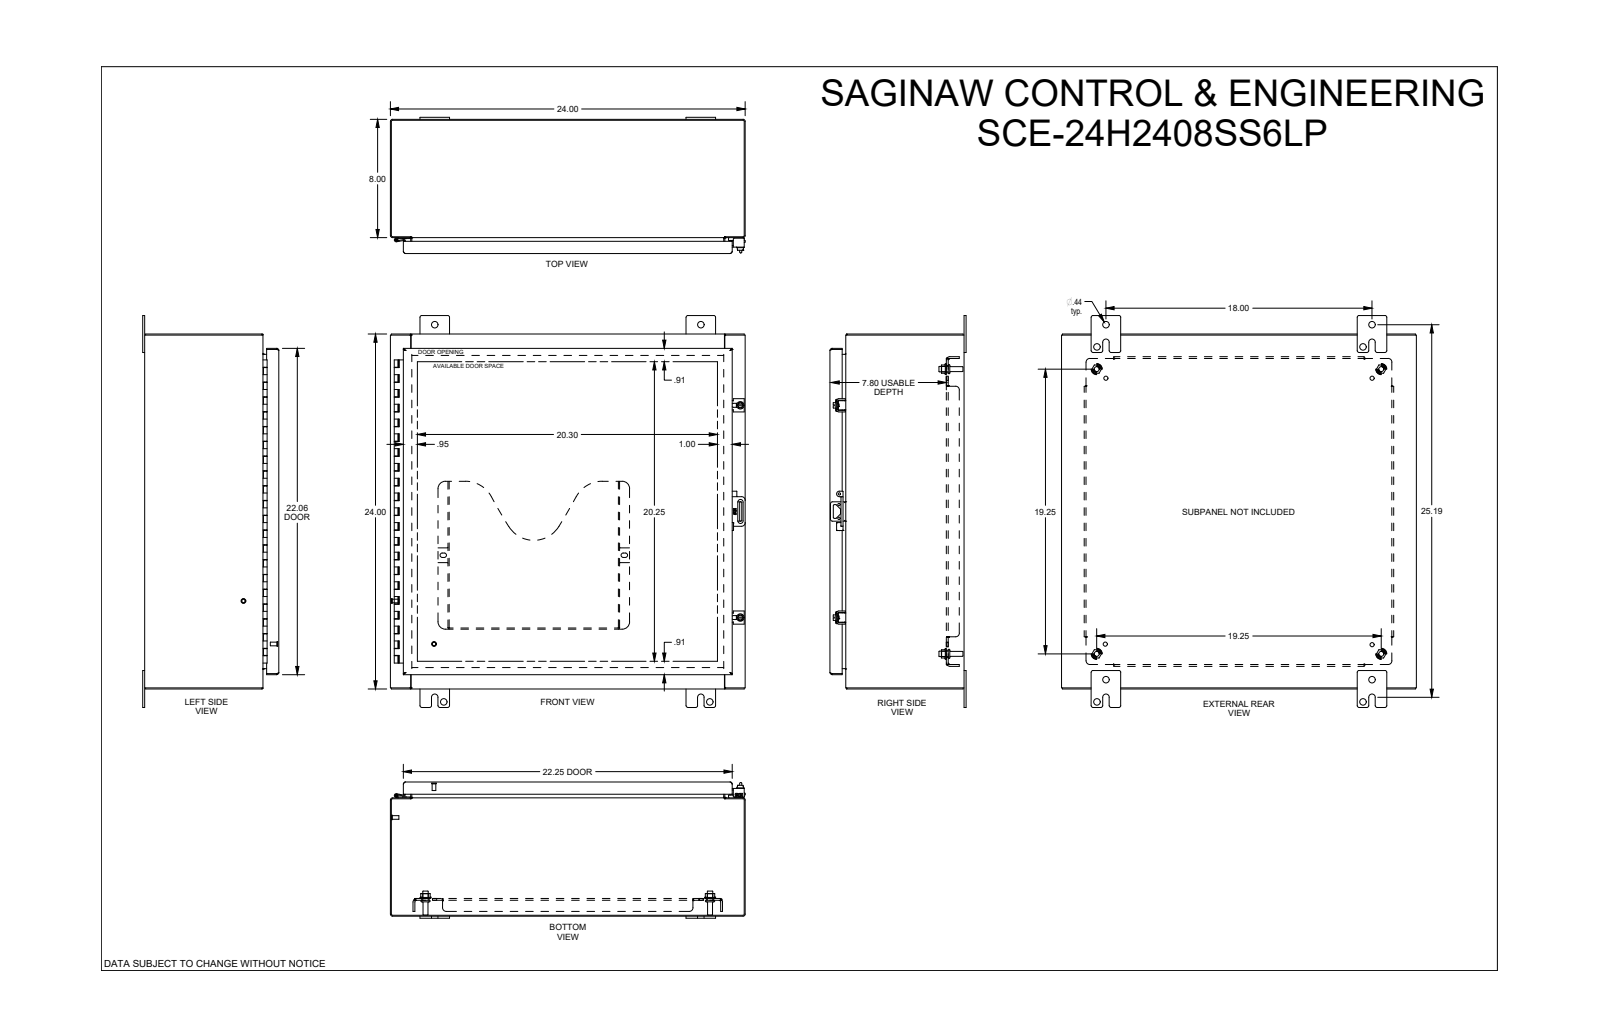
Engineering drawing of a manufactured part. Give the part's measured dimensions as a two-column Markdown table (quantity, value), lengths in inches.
| quantity | value |
| --- | --- |
| part name | SCE-24H2408SSLP |
| STEP written by | SolidWorks 2019 (CONFIG_CONTROL_DESIGN) |
| units | inches |
| bodies | 0 solids, 3192 faces (1285 planar, 670 cylindrical, 1237 other) |
| overall size | 26.5 × 24 × 9.208 |
| round holes (diameter × count) | 0.437 × 8, 0.25 × 5, 0.19 × 4, 0.193 × 4, 0.281 × 4, 0.367 × 4, 0.5 × 4, 0.16 × 2, 0.203 × 2, 0.13 × 1, 0.132 × 1 |
| round bosses / shafts (diameter × count) | 0.248 × 7, 0.563 × 5, 0.366 × 4, 0.332 × 4, 0.256 × 4, 0.188 × 4, 0.25 × 3, 0.507 × 2 |
| partial cylindrical surfaces (radius × count) | 0.01 × 114, 0.015 × 36, 0.029 × 30, 0.03 × 27, 0.125 × 27, 0.06 × 25, 0.04 × 22, 0.07 × 14 |
| main face-to-face distances | 0.075, 23.925, 8.998, 8.923, 0.075, 1.2, 7.873, 9.073, 8.998, 7.923 |
| hole center spacings | 18.641, 0.875, 18, 19.25, 6.5, 26.348, 0.515, 1.439 |
